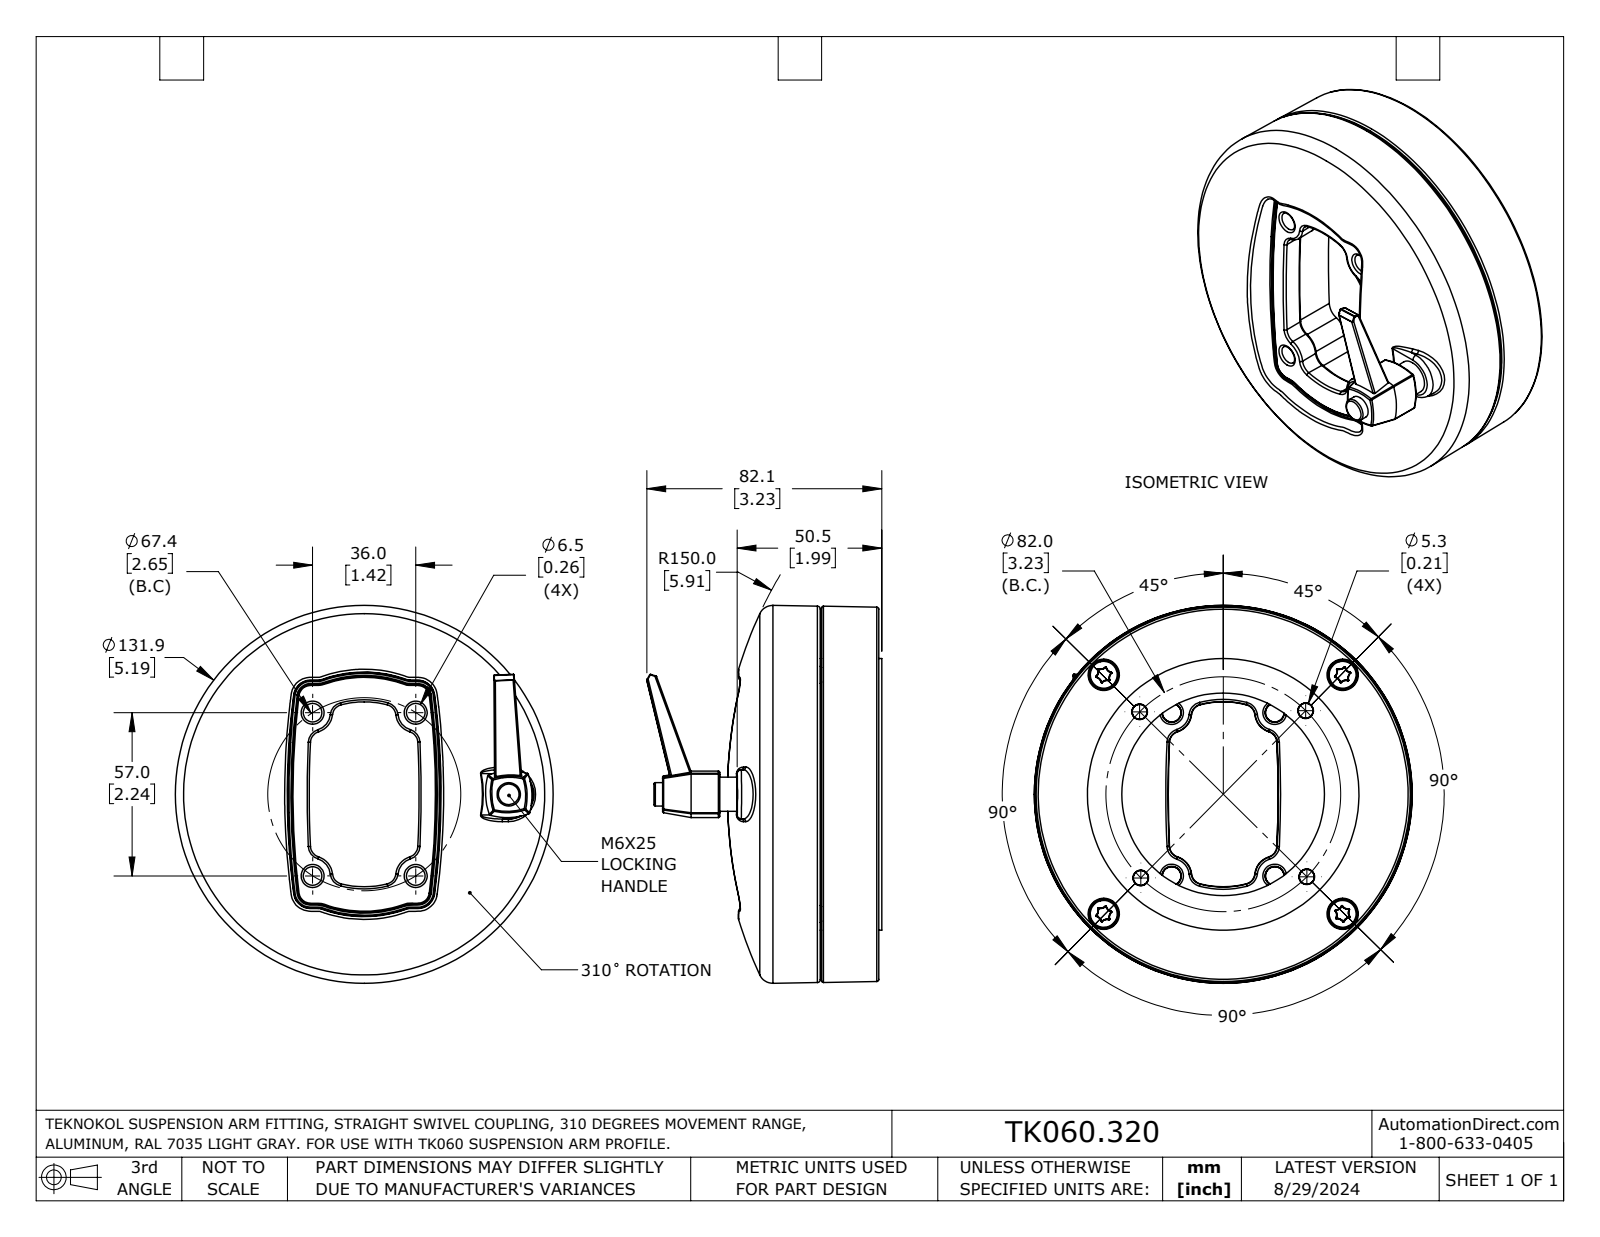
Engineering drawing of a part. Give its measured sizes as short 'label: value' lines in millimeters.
name: TK060.320
written by: SolidWorks 2023 (AUTOMOTIVE_DESIGN)
unit: mm
bodies: 2 solids, 1064 faces (195 planar, 185 cylindrical, 684 other)
size: 131.9 × 131.9 × 82.1
volume: 470 500 mm³; area: 84 450 mm²
holes: 4× ⌀5, 4× ⌀8.3, 1× ⌀8.7, 1× ⌀70.7
bosses: 5× ⌀6, 4× ⌀10, 1× ⌀94.8, 1× ⌀11.9, 1× ⌀8.2
rounds: 24× R0.1, 24× R2.5, 18× R1.5, 8× R0.5, 8× R4.9, 7× R0.2, 6× R1, 4× R6.1
face distances: 0.5, 20, 20.5, 21.5, 1, 21, 16.5, 1.5, 16, 36.5
hole spacings: 27.2, 33.7, 59, 61.2, 74.1, 83.4, 92.2, 36
